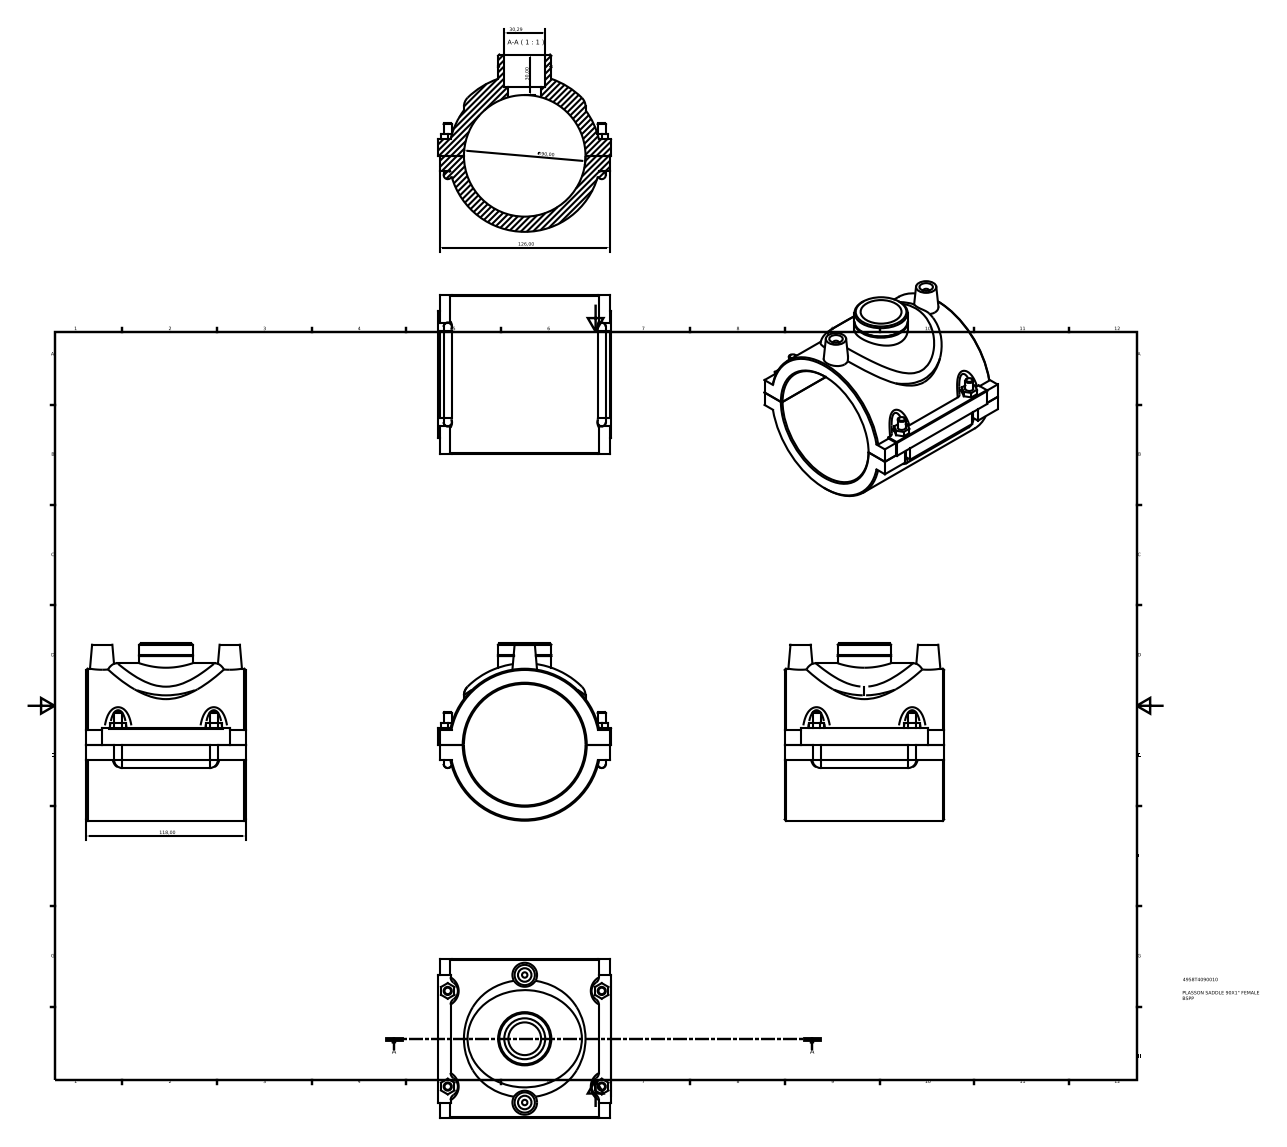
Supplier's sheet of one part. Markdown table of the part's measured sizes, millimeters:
| quantity | value |
| --- | --- |
| part name | 4958T4090010 |
| STEP written by | Autodesk Inventor 2015 (AUTOMOTIVE_DESIGN) |
| units | millimeters |
| bodies | 1 solid, 159 faces (86 planar, 39 cylindrical, 34 other) |
| overall size | 131.25 × 128 × 118 |
| volume | 496 920 mm³ |
| surface area | 105 746 mm² |
| round holes (diameter × count) | 10 × 2, 24.23 × 1, 30.29 × 1, 90 × 1 |
| round bosses / shafts (diameter × count) | 6 × 6, 4 × 2, 112.5 × 1, 39.38 × 1, 38.38 × 1 |
| partial cylindrical surfaces (radius × count) | 7.5 × 4, 0.5 × 1, 45 × 1, 60.3 × 1 |
| main face-to-face distances | 118, 1, 127, 11.2, 11.3, 23.5, 12.3, 12.2, 126, 128 |
| hole center spacings | 47.2, 94.4 |
